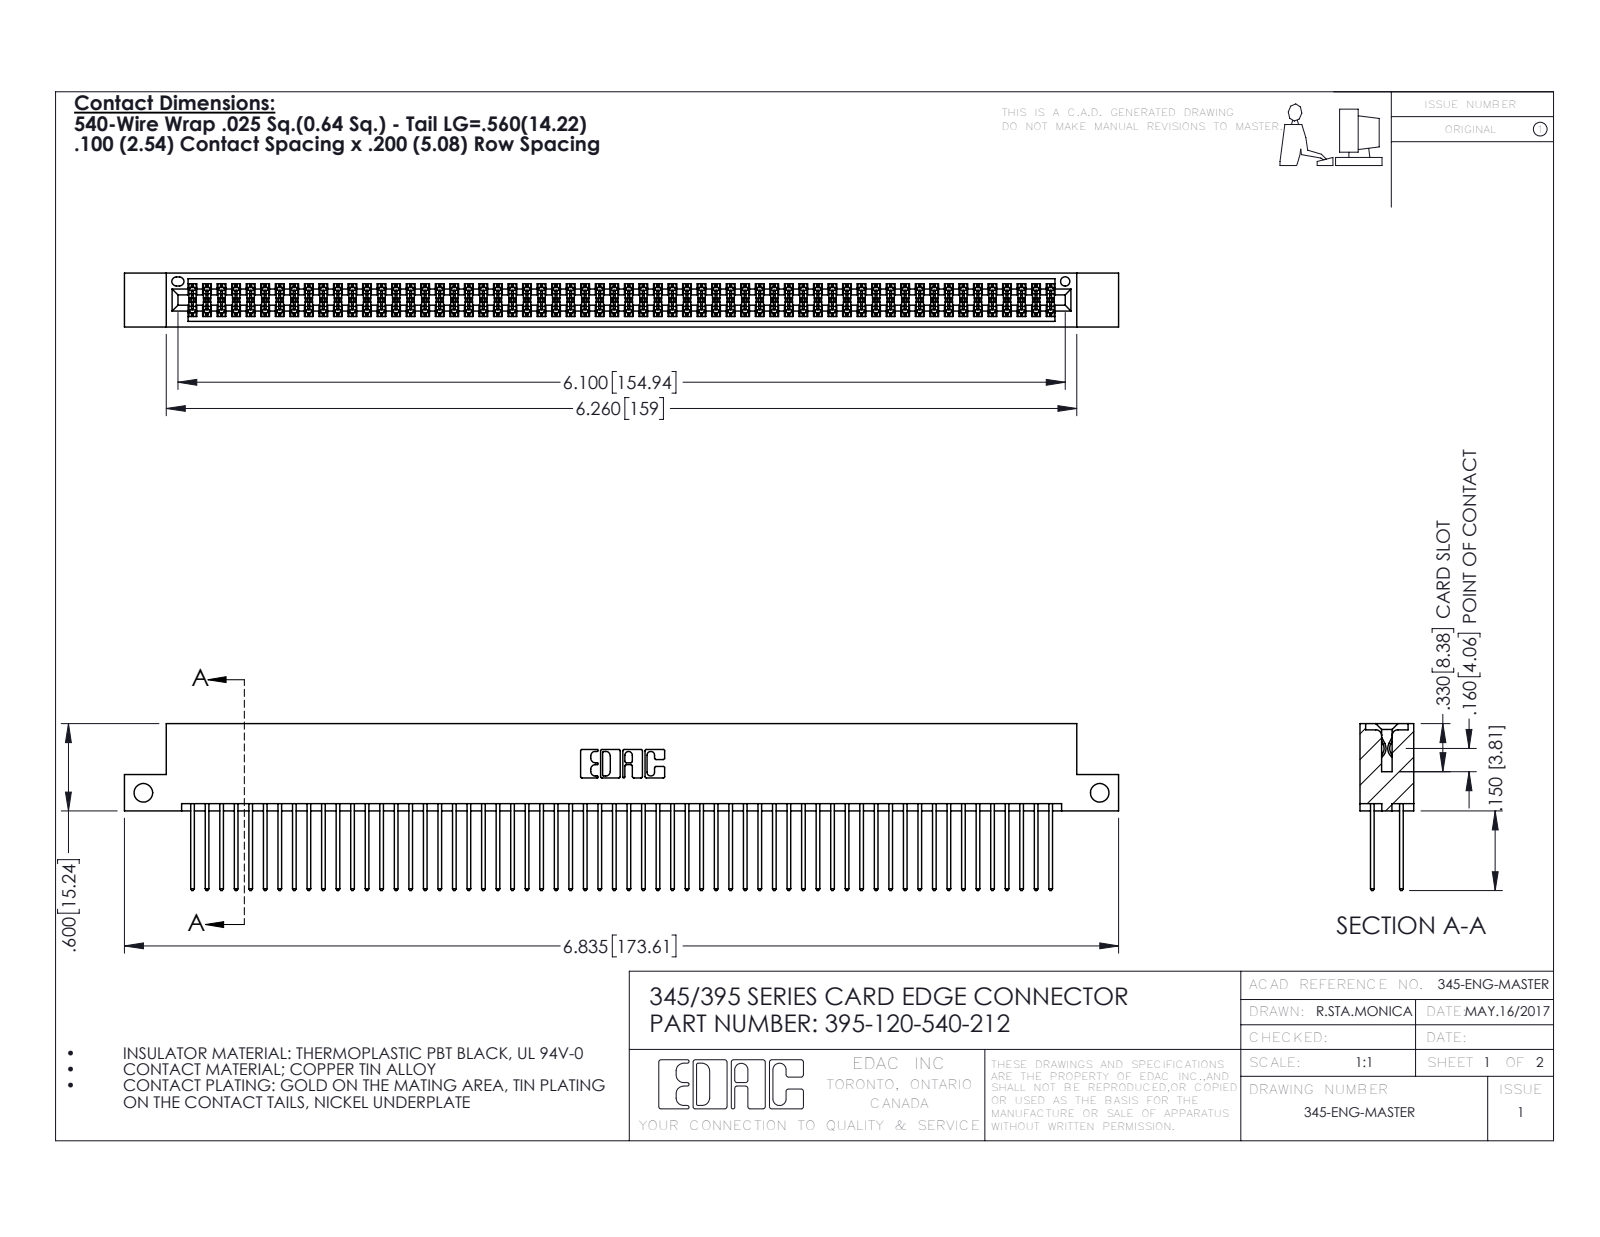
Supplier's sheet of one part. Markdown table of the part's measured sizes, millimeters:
| quantity | value |
| --- | --- |
| part name | 395-120-540-212; 345-292-001_345-293-140; 345 Part_Flush Mounting Lugs - Side Mount |
| STEP written by | SolidWorks 2016 (CONFIG_CONTROL_DESIGN) |
| units | millimeters |
| bodies | 121 solids, 6126 faces (4040 planar, 2086 cylindrical, 0 other) |
| overall size | 173.6 × 29.1 × 9.4 |
| volume | 17 400 mm³ |
| surface area | 28 050 mm² |
| round holes (diameter × count) | 3.3 × 2, 1.6 × 1 |
| partial cylindrical surfaces (radius × count) | 0.2 × 180, 0.3 × 120, 0.3 × 22, 0.2 × 6, 0.8 × 6, 0.7 × 3, 0.4 × 2, 0.5 × 2 |
| main face-to-face distances | 7.6, 1.8, 5.1, 2.5, 6.9, 0.6, 5.7, 9.4, 4.4, 3.8 |
| hole center spacings | 167 |
